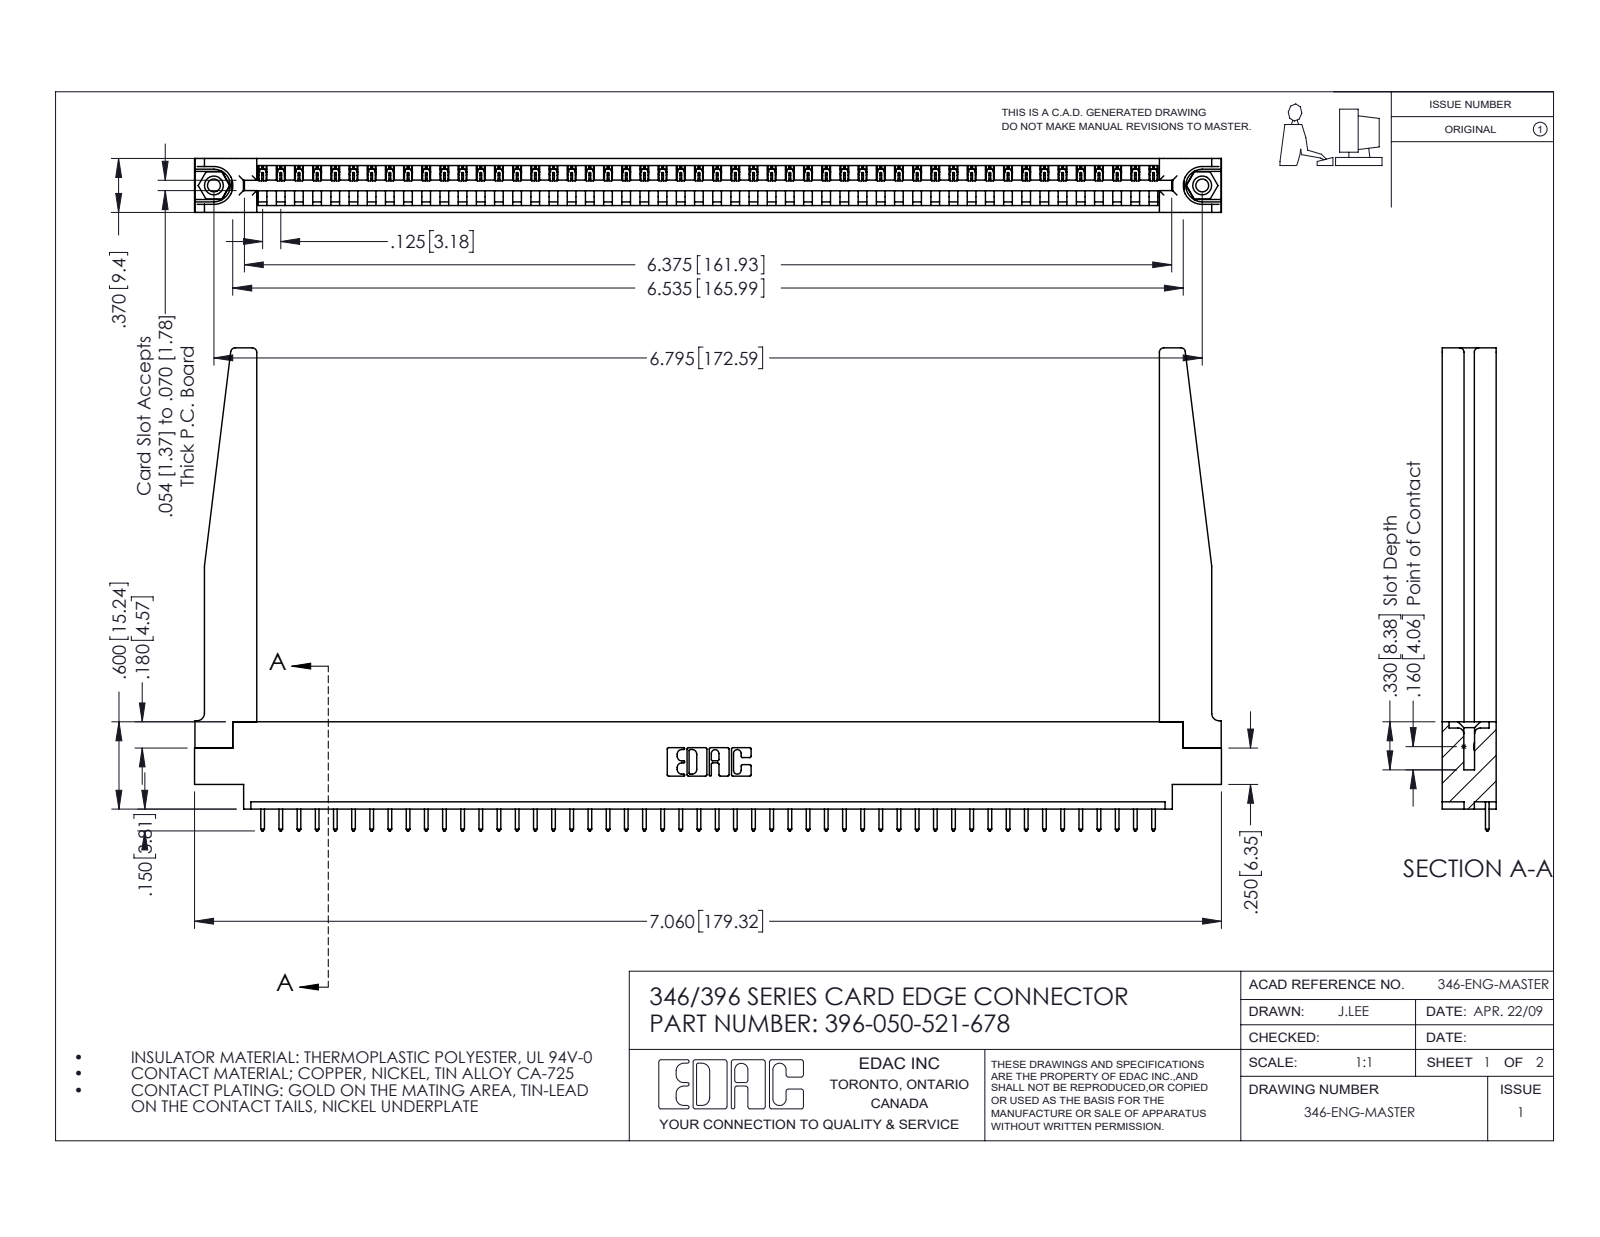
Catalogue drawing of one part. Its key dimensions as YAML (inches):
part_name: "346 Part_0.170 Offset - 0.156 Dia-TH; 346-220-078_345-220-078; 396-050-521-678; 345-292-001_345-293-121 (+1 more)"
step_written_by: "SolidWorks 2016 (CONFIG_CONTROL_DESIGN)"
units: inches
bodies: {solids: 55, faces: 3260, planar: 2222, cylindrical: 986, other: 52}
overall_size: [7.06, 3.32, 0.37]
volume: 1.454
surface_area: 42.43
round_holes:
  - {diameter: 0.089, count: 2}
  - {diameter: 0.125, count: 2}
  - {diameter: 0.156, count: 2}
  - {diameter: 0.064, count: 1}
round_bosses_or_shafts:
  - {diameter: 0.155, count: 2}
partial_cylinders:
  - {radius: 0.006, count: 100}
  - {radius: 0.01, count: 100}
  - {radius: 0.01, count: 22}
  - {radius: 0.03, count: 8}
  - {radius: 0.007, count: 6}
  - {radius: 0.031, count: 6}
  - {radius: 0.026, count: 3}
  - {radius: 0.031, count: 2}
face_to_face_distances: [0.37, 0.048, 0.322, 0.072, 0.148, 0.15, 0.25, 0.298, 0.025, 0.222]
hole_center_spacings: [0.246, 6.586, 6.795]
